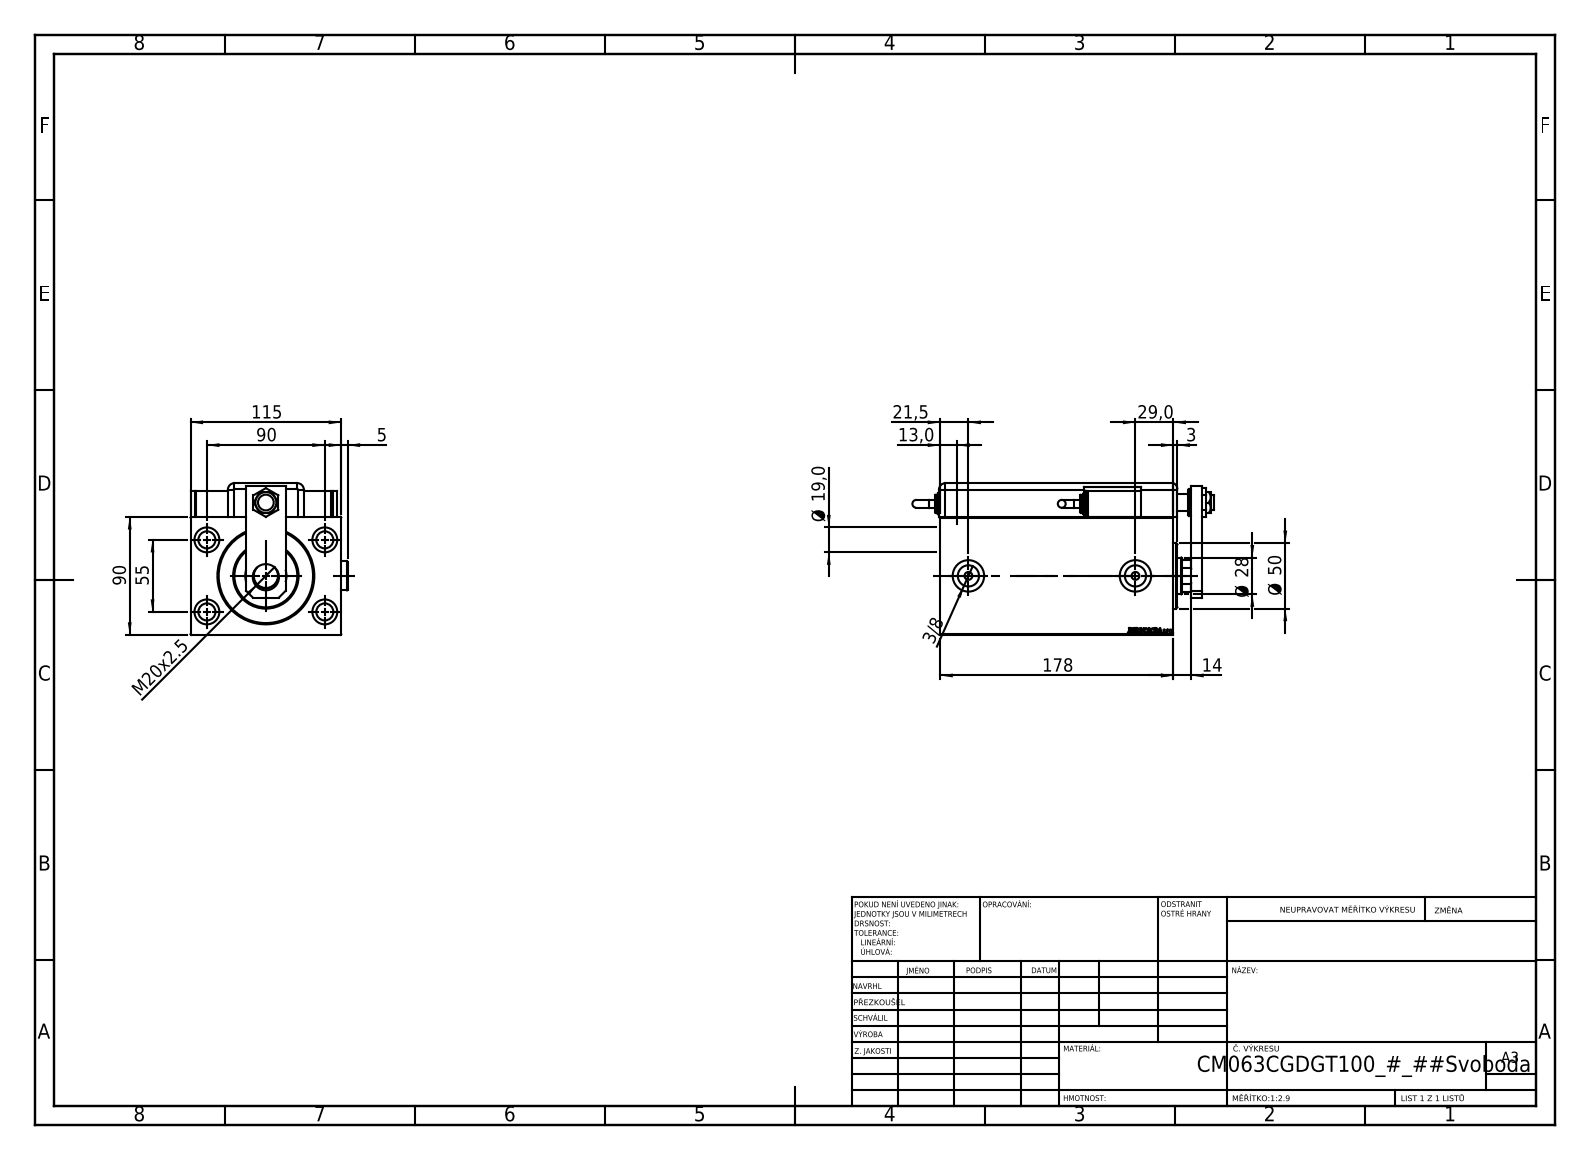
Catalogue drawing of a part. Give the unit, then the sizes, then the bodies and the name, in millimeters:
Units: millimetres
Overall size (bounding box): 230.46 × 119.9 × 115.8
Round holes (diameter × count): ⌀13 ×5, ⌀19 ×4, ⌀4 ×2, ⌀6 ×2, ⌀8 ×2, ⌀16.17 ×2, ⌀24 ×2, ⌀12 ×1, ⌀14 ×1, ⌀18.5 ×1, ⌀20 ×1, ⌀28 ×1
Round bosses / shafts (diameter × count): ⌀20 ×3, ⌀22 ×2, ⌀16 ×2, ⌀14 ×2, ⌀6 ×2, ⌀50 ×1
Partial cylindrical surfaces — rounded edges, fillets, slot ends (radius × count): R5 ×9, R10 ×1, R13.5 ×1
Main face-to-face distances: 90, 3, 115, 178, 25.8, 115.8, 28.5, 112.8, 22.8, 17.5
Hole centre spacings: 52.74, 53.27, 52.22, 55, 90, 94.85, 105.48, 1
Volume: 1 658 000 mm³ · Surface area: 275 696 mm²
Bodies: 15 solids, 1303 faces (649 planar, 133 cylindrical, 521 other)
Part name (STEP PRODUCT): SWITCH DIM A_G; MAGNETIC SWITCH Q; Zatka_OIL_PORT; SWITCH Q (+7 more)
STEP written by: SolidWorks 2019 (CONFIG_CONTROL_DESIGN)
